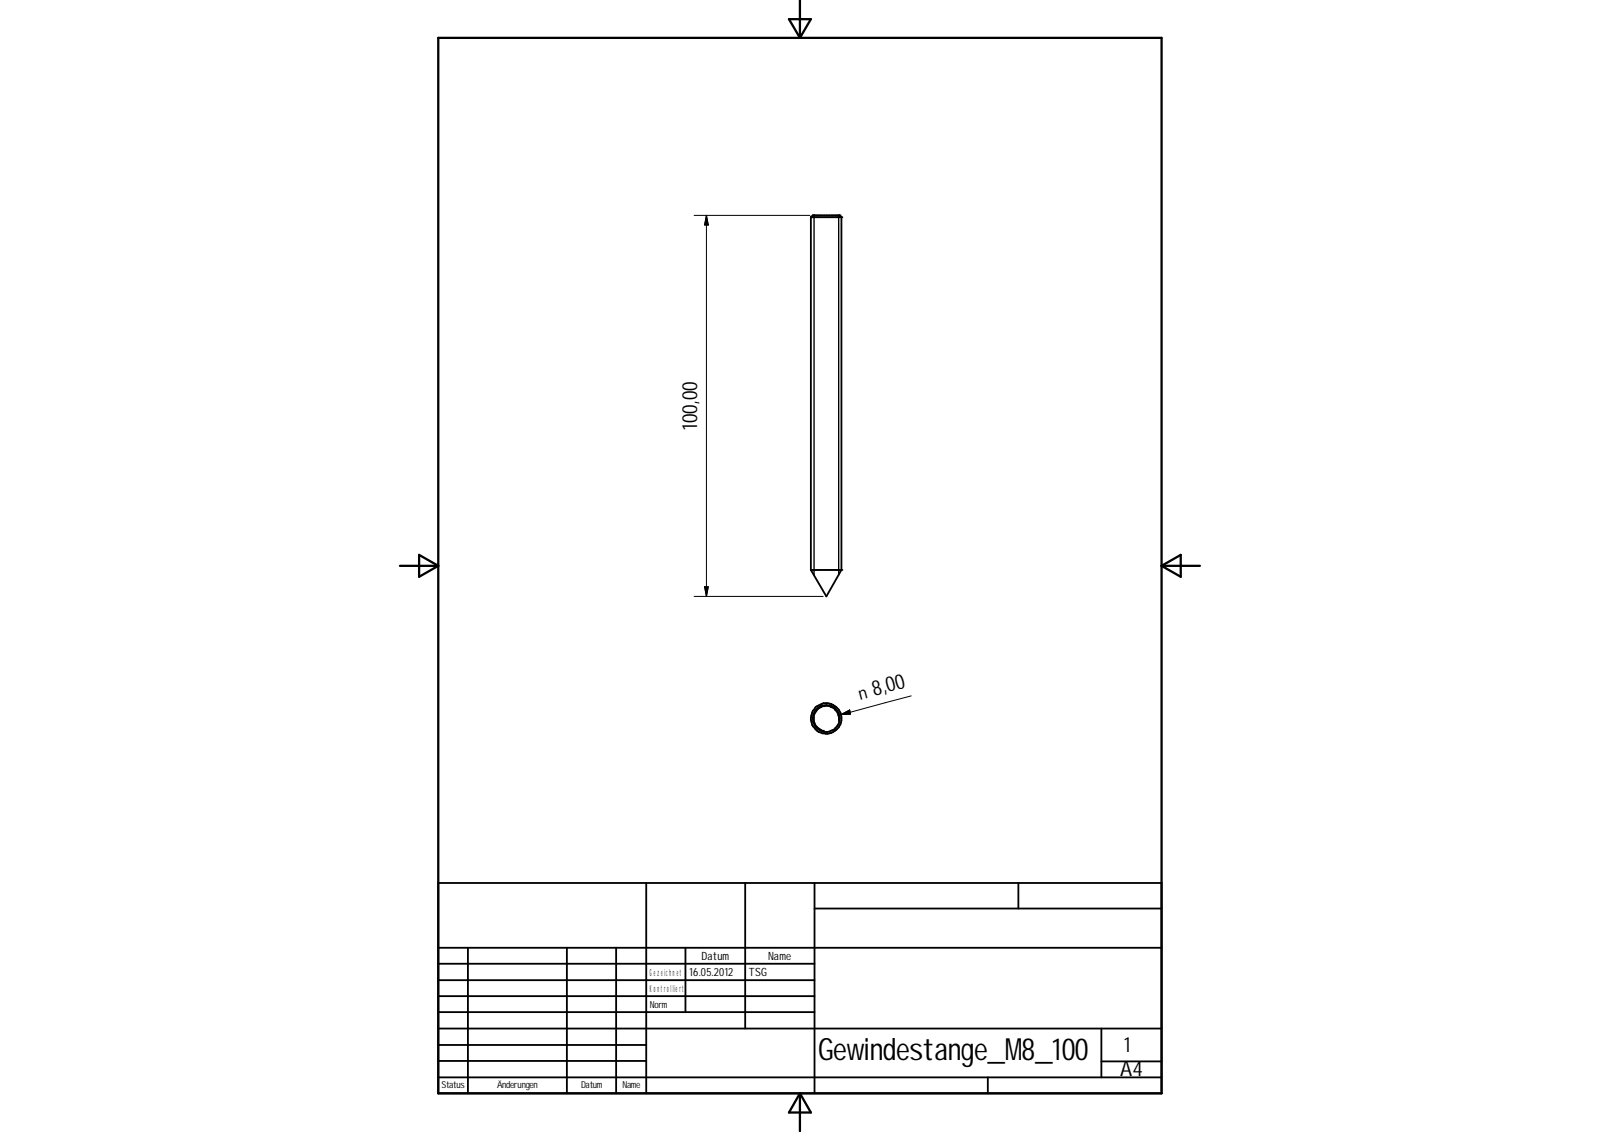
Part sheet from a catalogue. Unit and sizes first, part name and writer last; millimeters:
Units: millimetres
Overall size (bounding box): 550 × 215 × 86.3
Round holes (diameter × count): ⌀6.65 ×3, ⌀8.4 ×2, ⌀8 ×1
Round bosses / shafts (diameter × count): ⌀24 ×2, ⌀11.63 ×2, ⌀8 ×2, ⌀10 ×1
Partial cylindrical surfaces — rounded edges, fillets, slot ends (radius × count): R6 ×4
Main face-to-face distances: 19, 38, 57, 135, 150, 50, 100, 21, 40, 59
Hole centre spacings: 85
Volume: 1 606 000 mm³ · Surface area: 234 569 mm²
Bodies: 16 solids, 198 faces (113 planar, 23 cylindrical, 62 other)
Part name (STEP PRODUCT): Startrampe_Fu\S\; Standbein_Fu\S\; Standbein_Block_Halter; Standbein_Kupferrohr (+5 more)
STEP written by: unknown (AUTOMOTIVE_DESIGN)
